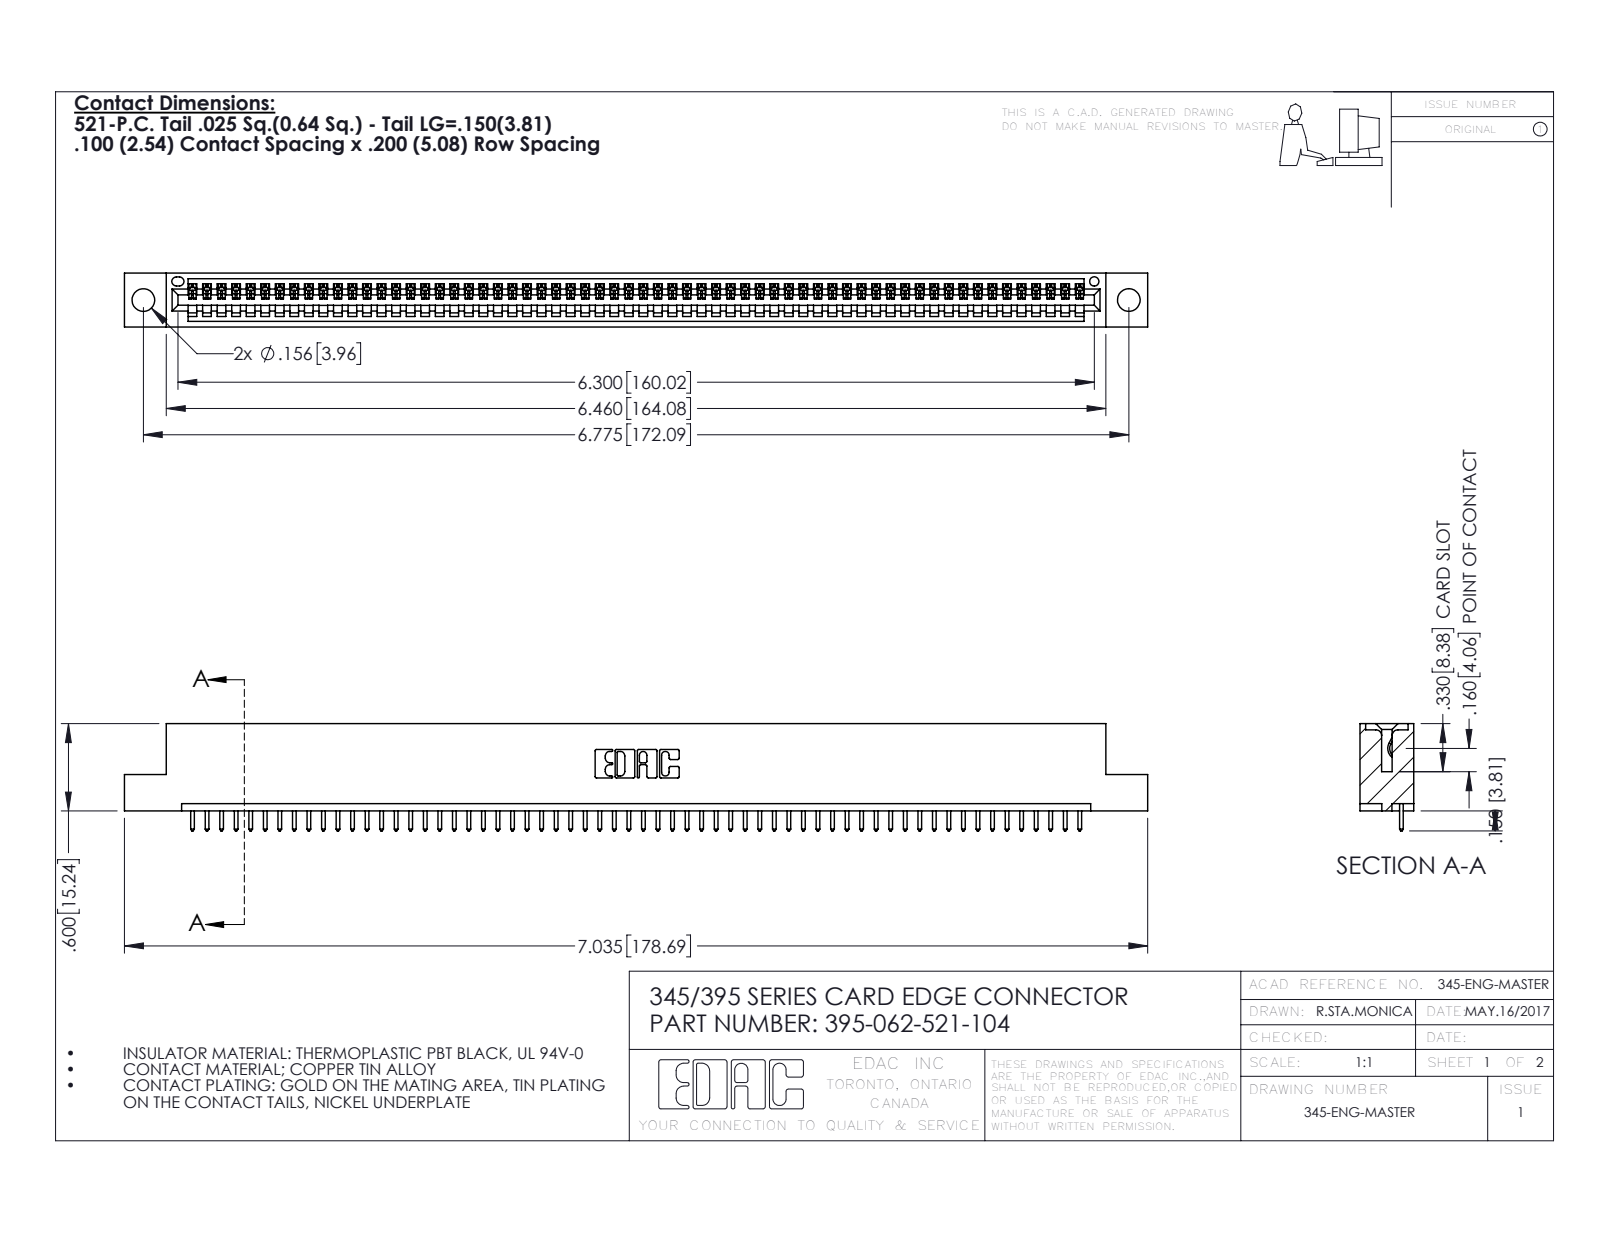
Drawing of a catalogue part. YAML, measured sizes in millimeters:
part_name: "395-062-521-104; 345-292-001_345-293-121; 345 Part_Flush Mounting Lugs - 0.156 Dia-TH"
step_written_by: "SolidWorks 2016 (CONFIG_CONTROL_DESIGN)"
units: millimeters
bodies: {solids: 63, faces: 3722, planar: 2560, cylindrical: 1162, other: 0}
overall_size: [178.7, 18.7, 9.4]
volume: 16880
surface_area: 21810
round_holes:
  - {diameter: 4, count: 2}
  - {diameter: 1.6, count: 1}
partial_cylinders:
  - {radius: 0.2, count: 124}
  - {radius: 0.3, count: 124}
  - {radius: 0.3, count: 22}
  - {radius: 0.2, count: 6}
  - {radius: 0.8, count: 6}
  - {radius: 0.7, count: 3}
  - {radius: 0.8, count: 2}
  - {radius: 1, count: 2}
face_to_face_distances: [7.6, 1.8, 9.4, 5.1, 2.5, 6.9, 0.6, 5.7, 3.8, 1.8]
hole_center_spacings: [6.9, 166.1, 172.1]
